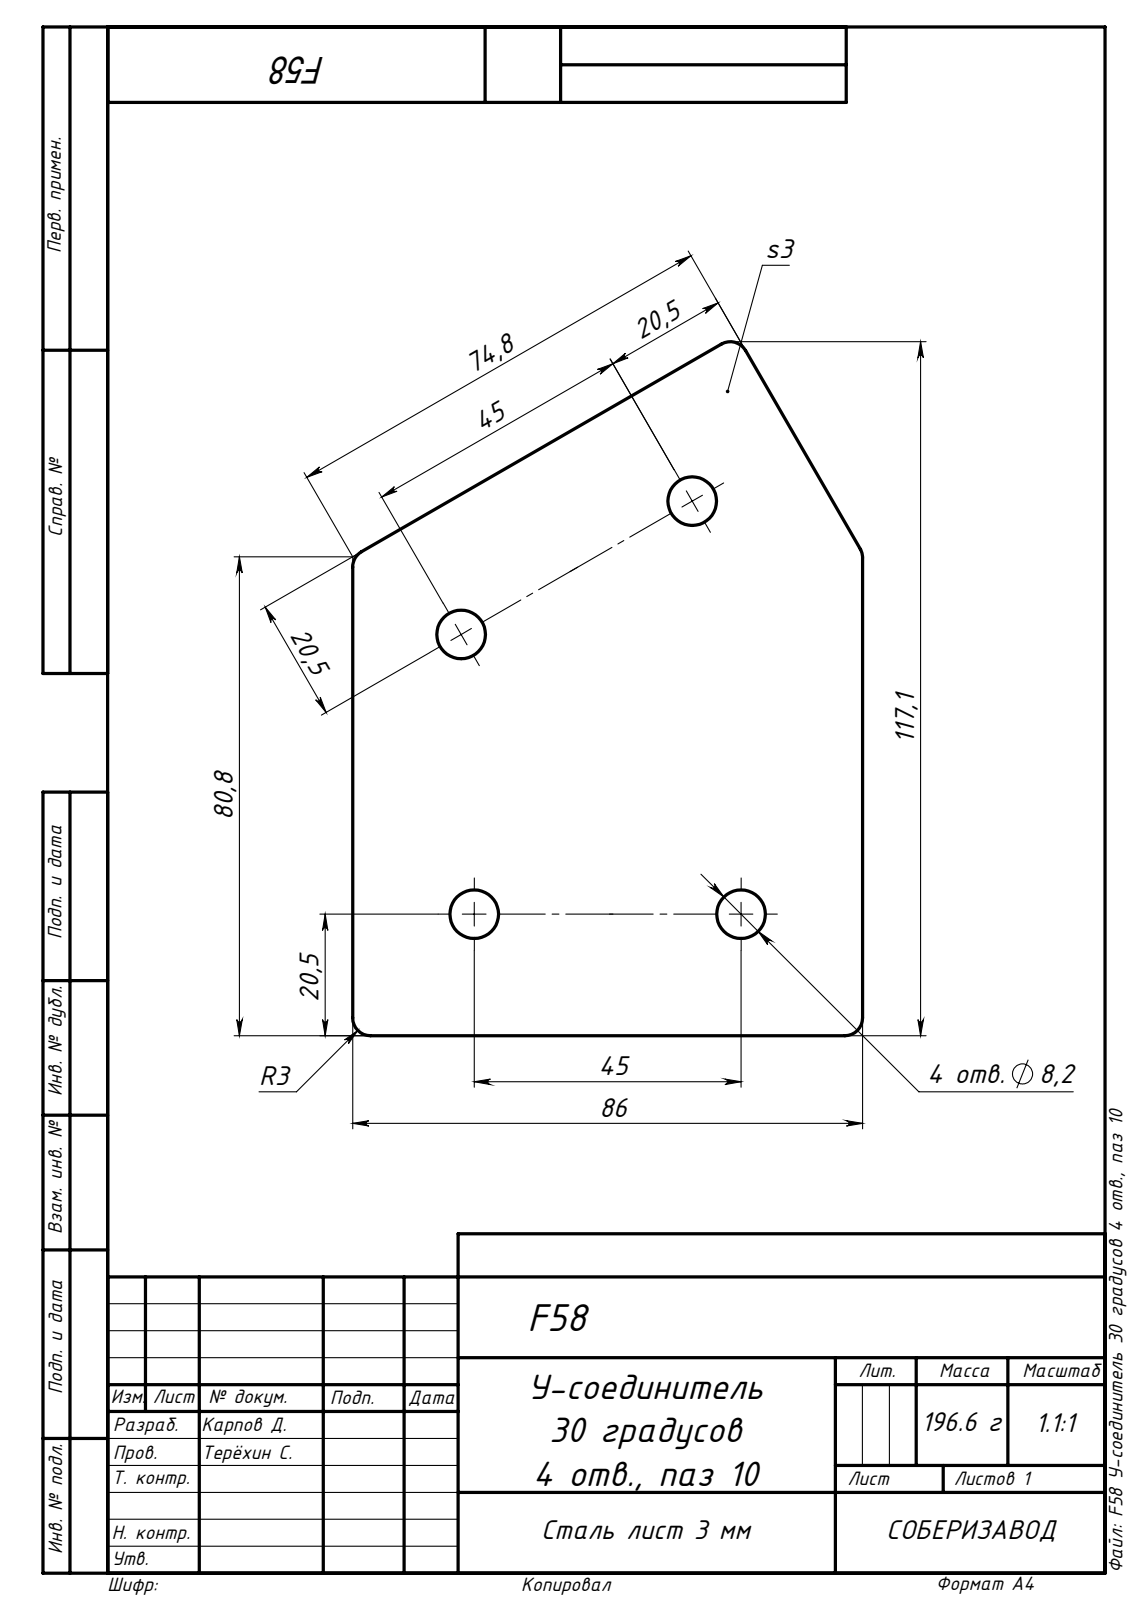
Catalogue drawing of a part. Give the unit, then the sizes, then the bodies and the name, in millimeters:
Units: millimetres
Overall size (bounding box): 117.11 × 86 × 3
Round holes (diameter × count): ⌀8.2 ×4
Partial cylindrical surfaces — rounded edges, fillets, slot ends (radius × count): R3 ×5
Main face-to-face distances: 3, 86
Hole centre spacings: 45, 45.01, 47.26, 66.77, 70.19, 78.81
Volume: 25 041 mm³ · Surface area: 18 087 mm²
Bodies: 1 solid, 20 faces (7 planar, 13 cylindrical, 0 other)
Part name (STEP PRODUCT): F58 У-соединитель 30 градусов 4 отв., паз 10
STEP written by: SolidWorks 2020 (AUTOMOTIVE_DESIGN)
